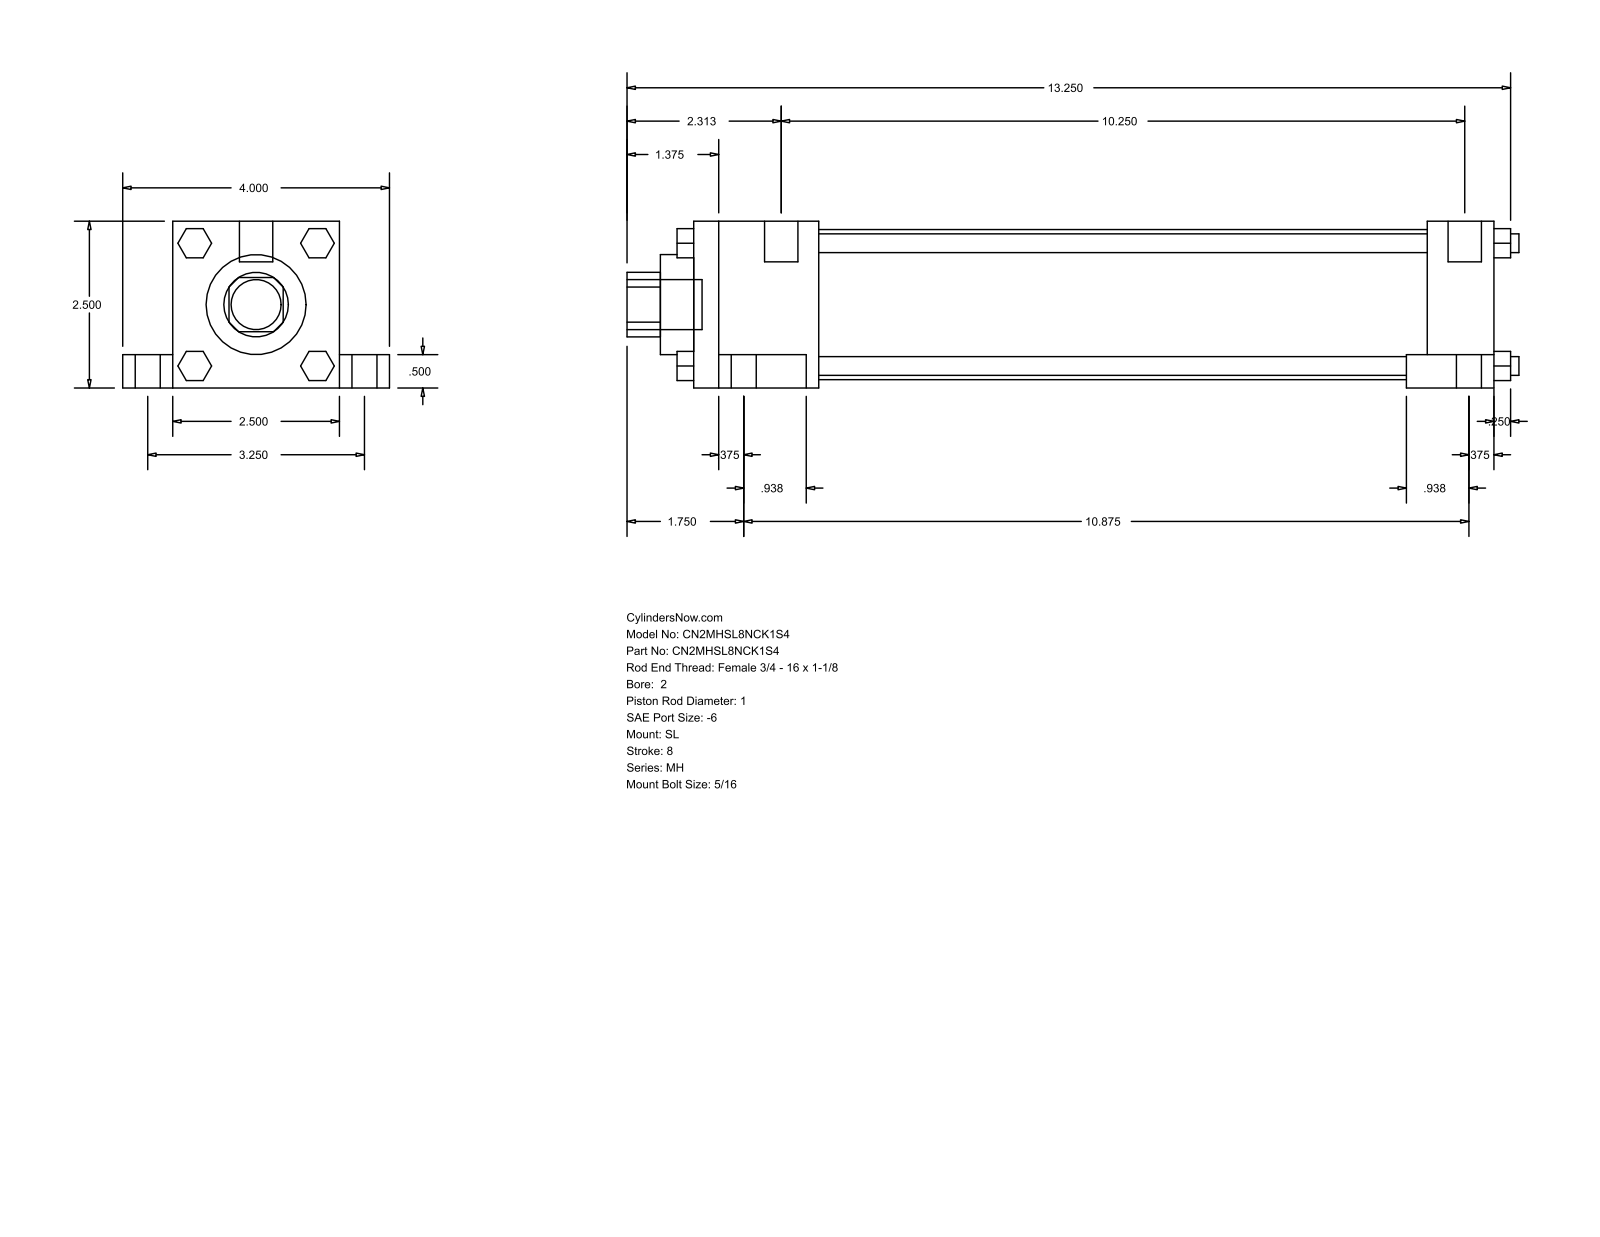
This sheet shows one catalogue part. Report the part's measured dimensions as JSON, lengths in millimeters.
{"part_name": "MH_SL__0200_1", "step_written_by": "GSSL Pune (CONFIG_CONTROL_DESIGN)", "units": "millimeters", "bodies": {"solids": 0, "faces": 148, "planar": 112, "cylindrical": 36, "other": 0}, "overall_size": [339.73, 101.6, 63.5], "round_holes": [[25.4, 1], [38.1, 1], [57.15, 1]], "round_bosses_or_shafts": [[15.88, 4], [9.53, 4], [7.14, 4], [5.56, 4], [12.7, 2], [19.05, 1]], "partial_cylinders_radius": [[12.29, 1]], "face_to_face_distances": [63.5, 304.8, 12.7, 19.05, 50.8, 82.55, 25.4, 9.52, 279.4, 47.63]}
